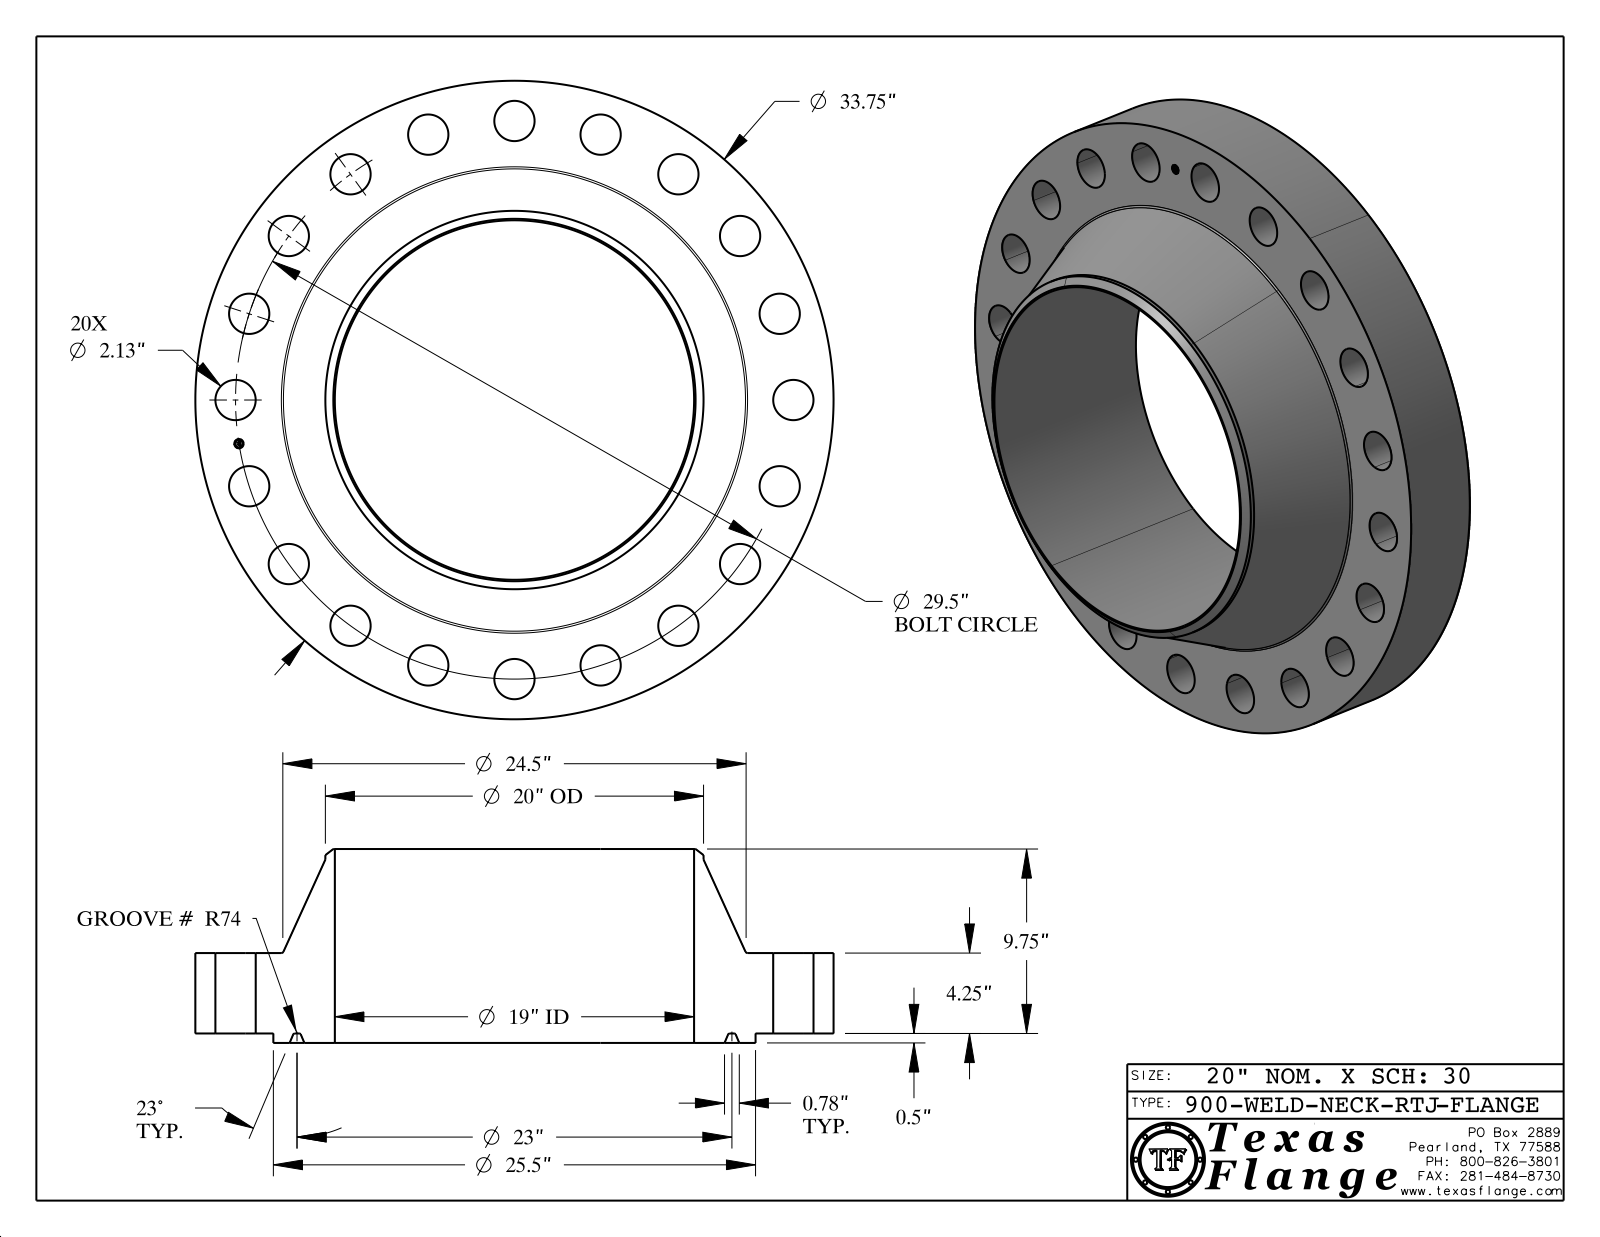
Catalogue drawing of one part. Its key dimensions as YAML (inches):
part_name: "900-WELD-NECK-RTJ"
step_written_by: "CATIA V5 STEP AP214 (AUTOMOTIVE_DESIGN)"
units: inches
bodies: {solids: 1, faces: 453, planar: 371, cylindrical: 68, other: 14}
overall_size: [33.75, 33.75, 10.25]
volume: 2927
surface_area: 3040
round_holes:
  - {diameter: 2.13, count: 20}
  - {diameter: 0.495, count: 1}
  - {diameter: 19, count: 1}
round_bosses_or_shafts:
  - {diameter: 0.03, count: 8}
  - {diameter: 33.75, count: 1}
  - {diameter: 25.5, count: 1}
  - {diameter: 20, count: 1}
  - {diameter: 0.39, count: 1}
face_to_face_distances: [4.25, 0.5, 4.75, 10.25, 9.75, 5.5, 4.735, 4.235, 0.015, 5.515]
hole_center_spacings: [14.75, 29.137, 4.615, 17.34, 20.859, 23.866, 26.285, 9.116]
